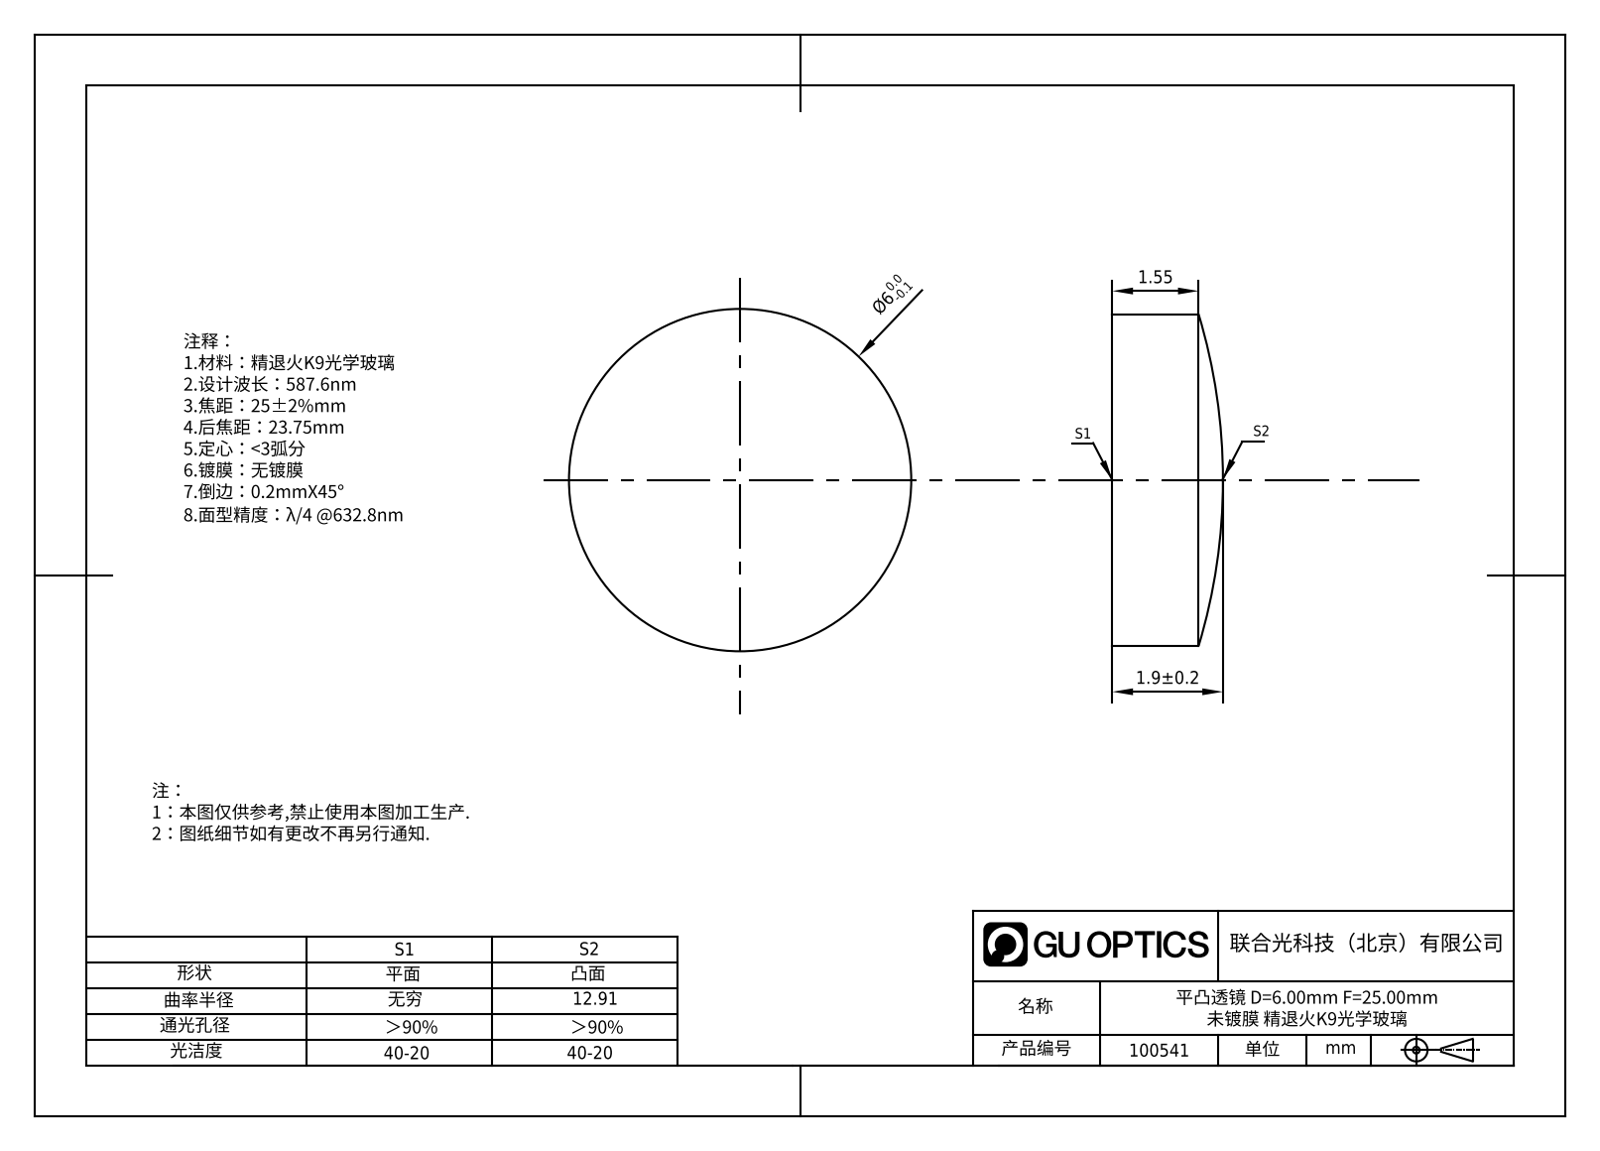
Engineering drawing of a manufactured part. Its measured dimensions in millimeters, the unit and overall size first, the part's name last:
Units: millimetres
Overall size (bounding box): 6 × 6 × 2.29
Round bosses / shafts (diameter × count): ⌀6 ×1
Volume: 54 mm³ · Surface area: 87 mm²
Bodies: 1 solid, 5 faces (1 planar, 2 cylindrical, 2 other)
Part name (STEP PRODUCT): 100541
STEP written by: SolidWorks 2020 (CONFIG_CONTROL_DESIGN)
